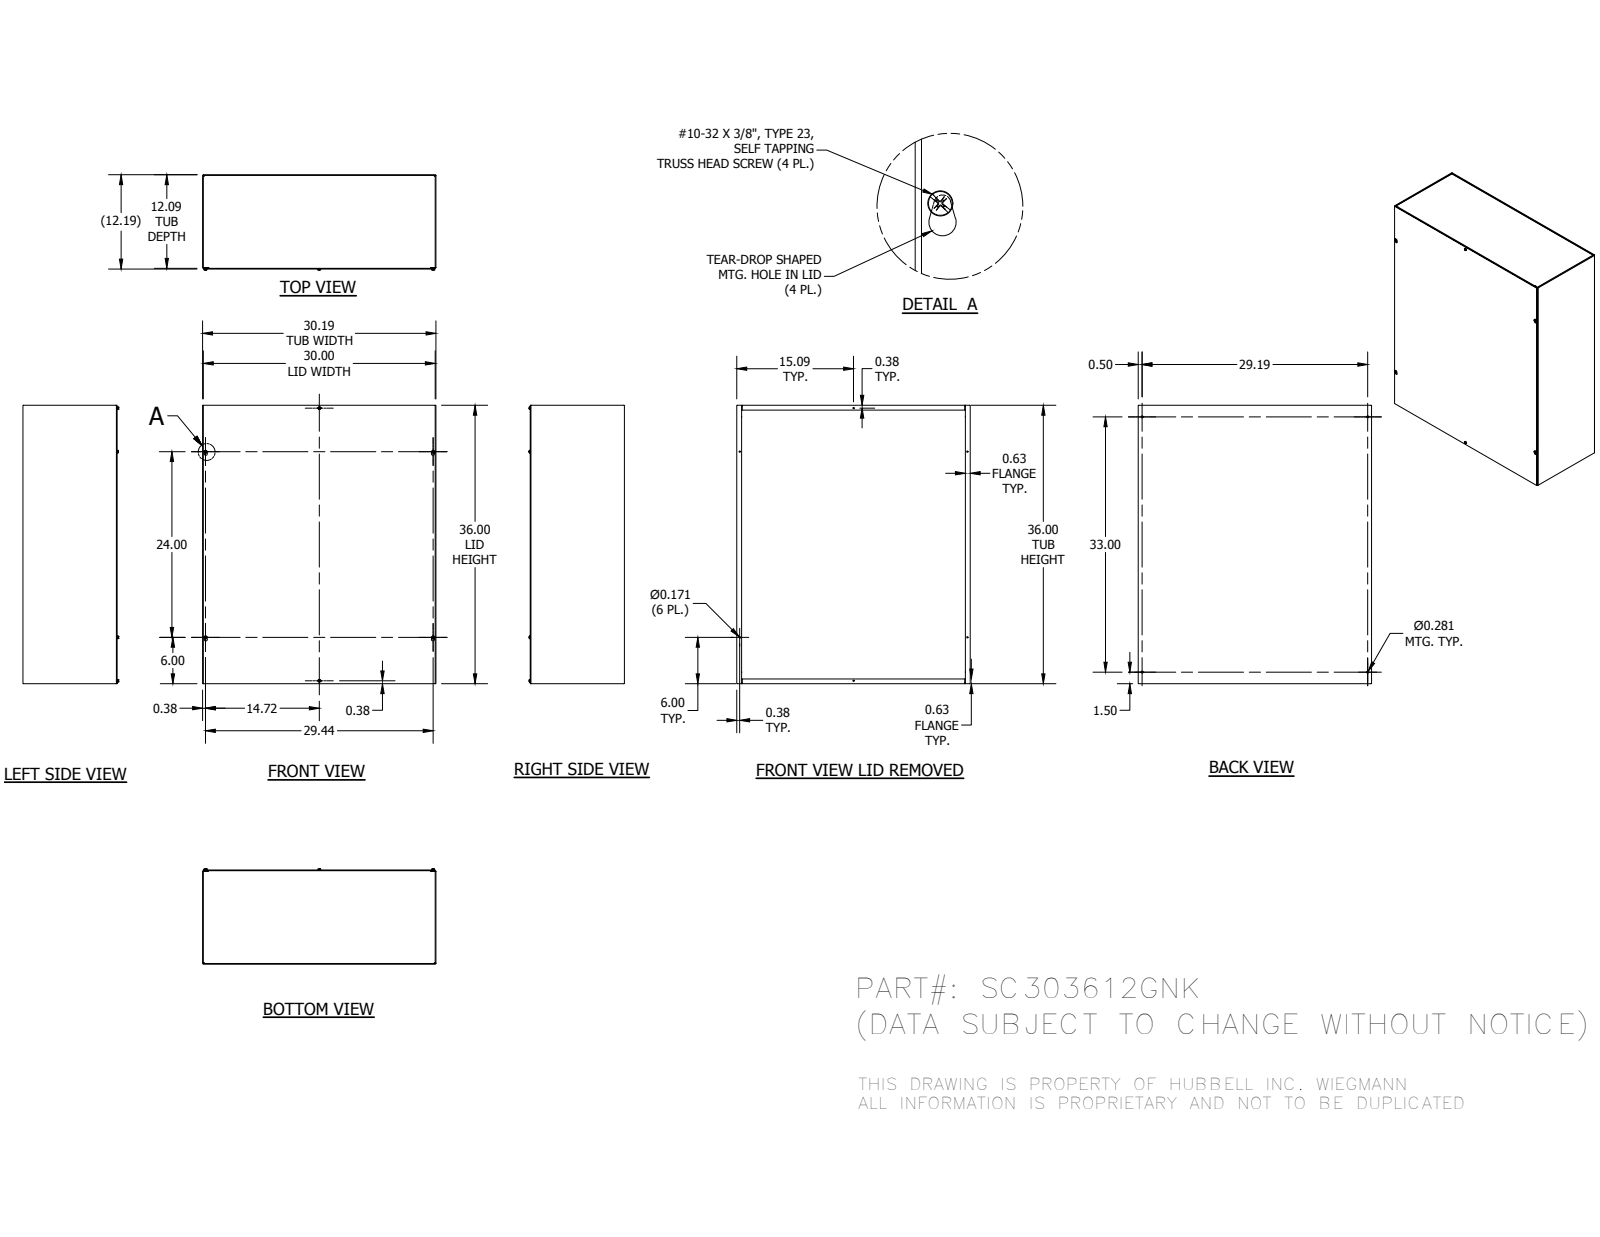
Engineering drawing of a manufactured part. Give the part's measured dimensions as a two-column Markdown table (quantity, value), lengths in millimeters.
| quantity | value |
| --- | --- |
| part name | SC303612GNKBLR; SC3012GNKTB; SC3036GLPA; 37214 (+1 more) |
| STEP written by | Autodesk Inventor 2014 (AUTOMOTIVE_DESIGN) |
| units | millimeters |
| bodies | 10 solids, 404 faces (232 planar, 50 cylindrical, 122 other) |
| overall size | 914.4 × 766.76 × 312.91 |
| volume | 5 942 000 mm³ |
| surface area | 5 022 000 mm² |
| round holes (diameter × count) | 4.34 × 6, 7.14 × 4, 7.92 × 2 |
| round bosses / shafts (diameter × count) | 4.83 × 6 |
| partial cylindrical surfaces (radius × count) | 0.4 × 12, 2.78 × 12, 3.17 × 4, 5.16 × 4 |
| main face-to-face distances | 2.38, 307.18, 304.8, 309.56, 764.38, 912.02, 762, 766.76, 914.4, 909.64 |
| hole center spacings | 371.78, 400.23, 942.71, 114.34, 723.91, 753.26, 840.23, 1038.45 |
